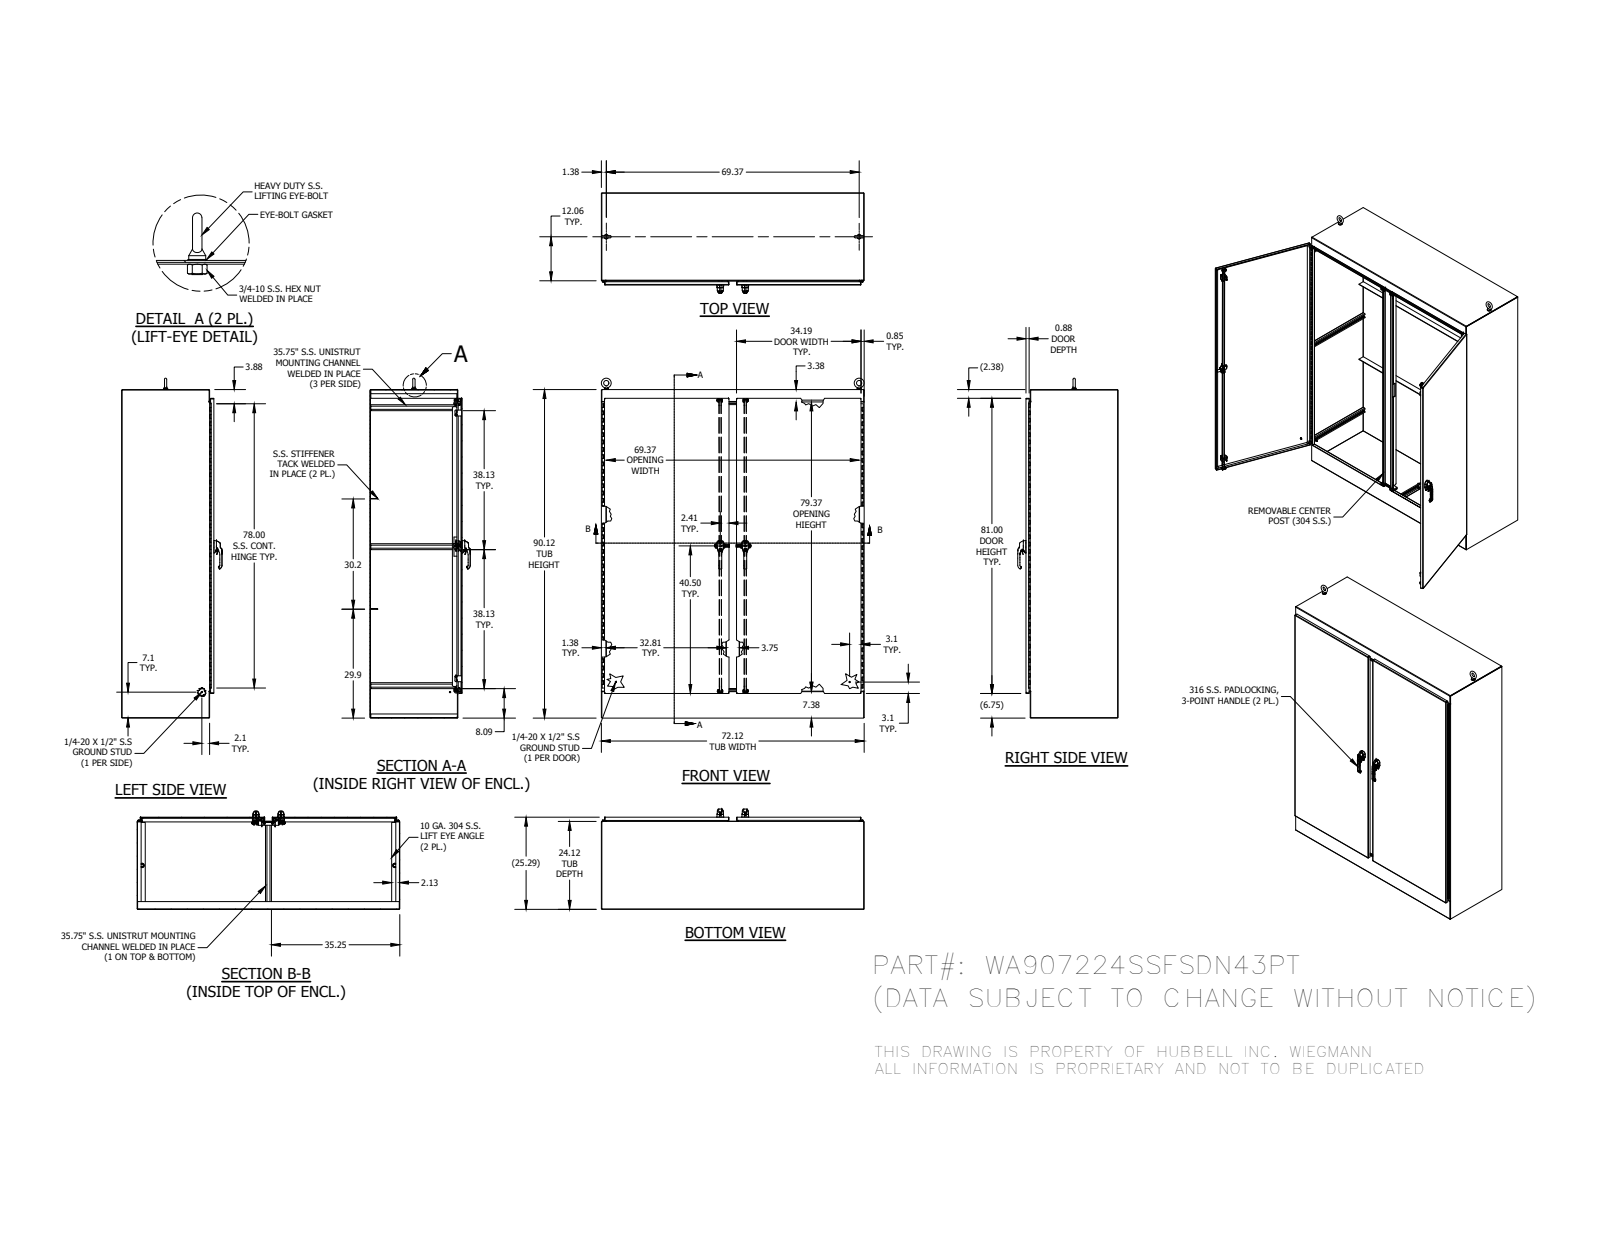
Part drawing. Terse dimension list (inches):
name: HFW3762; 328131T-78; 1091-74-01; D125B_10_5 (+8 more)
written by: SolidWorks 2014 (AUTOMOTIVE_DESIGN)
unit: in
bodies: 133 solids, 7276 faces (2800 planar, 2780 cylindrical, 1696 other)
size: 93.248 × 72.125 × 27.541
volume: 3 062 in³; area: 49 873 in²
holes: 16× ⌀0.262, 16× ⌀0.375, 8× ⌀0.187, 6× ⌀0.213, 6× ⌀0.25, 6× ⌀0.281, 4× ⌀0.196, 4× ⌀0.241, 4× ⌀0.252, 4× ⌀0.281, 4× ⌀0.315, 4× ⌀0.4
bosses: 7× ⌀0.25, 6× ⌀1, 6× ⌀0.533, 6× ⌀0.236, 4× ⌀0.563, 4× ⌀0.531, 4× ⌀0.5, 4× ⌀0.438
rounds: 350× R0.02, 213× R0.012, 44× R0.019, 44× R0.125, 34× R0.05, 28× R0.079, 24× R0.025, 24× R0.059
face distances: 0.125, 0.125, 25.167, 72, 90, 25.165, 25.04, 25.042, 25.29, 25.165
hole spacings: 72.49, 73.24, 26, 0.38, 0.38, 8.667, 0.76, 17.333
